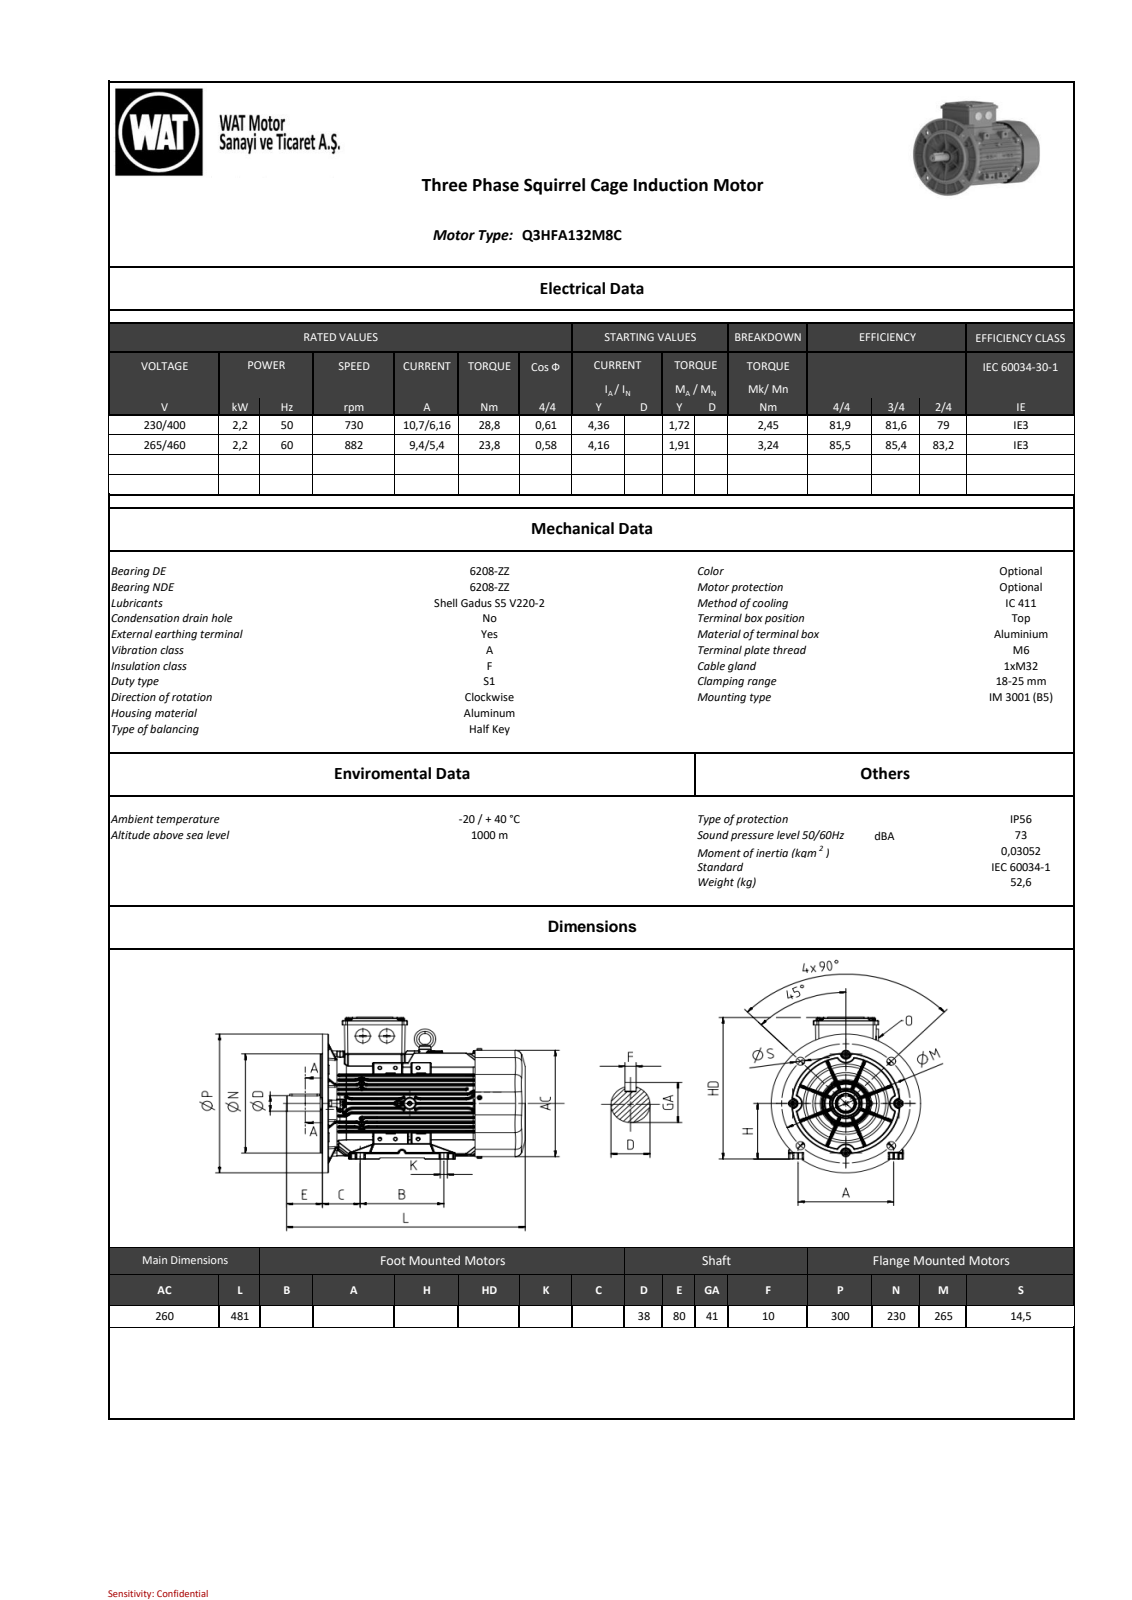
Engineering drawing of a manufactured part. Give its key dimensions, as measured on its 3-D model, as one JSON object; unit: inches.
{"part_name": "QH series_ 132_B5_stp_objects", "step_written_by": "SIEMENS PLM Software NX2206.8101 (AP203_CONFIGURATION_CONTROLLED_3D_DESIGN_OF_MECHANICAL_PARTS_AND_ASSEMBLIES_MIM_LF)", "units": "inches", "bodies": {"solids": 0, "faces": 6165, "planar": 1517, "cylindrical": 2700, "other": 1948}, "overall_size": [18.917, 13.393, 11.809], "round_holes": [[0.333, 2], [0.334, 1], [0.334, 1], [0.472, 1], [0.551, 1], [0.961, 1], [3.228, 1], [3.386, 1], [7.087, 1]], "round_bosses_or_shafts": [[0.315, 11], [0.512, 4], [1.496, 3], [9.075, 1], [9.055, 1], [3.416, 1], [1.772, 1], [1.575, 1]], "partial_cylinders_radius": [[0.031, 910], [0.039, 523], [0.02, 104], [0.118, 72], [0.079, 49], [0.197, 18], [2.362, 16], [1.024, 12]], "face_to_face_distances": [0.41, 0.416, 0.059, 0.82, 0.405, 4.944, 3.309, 4.535, 4.13, 0.374], "hole_center_spacings": [3.517, 4.921, 5.803, 7.044]}
